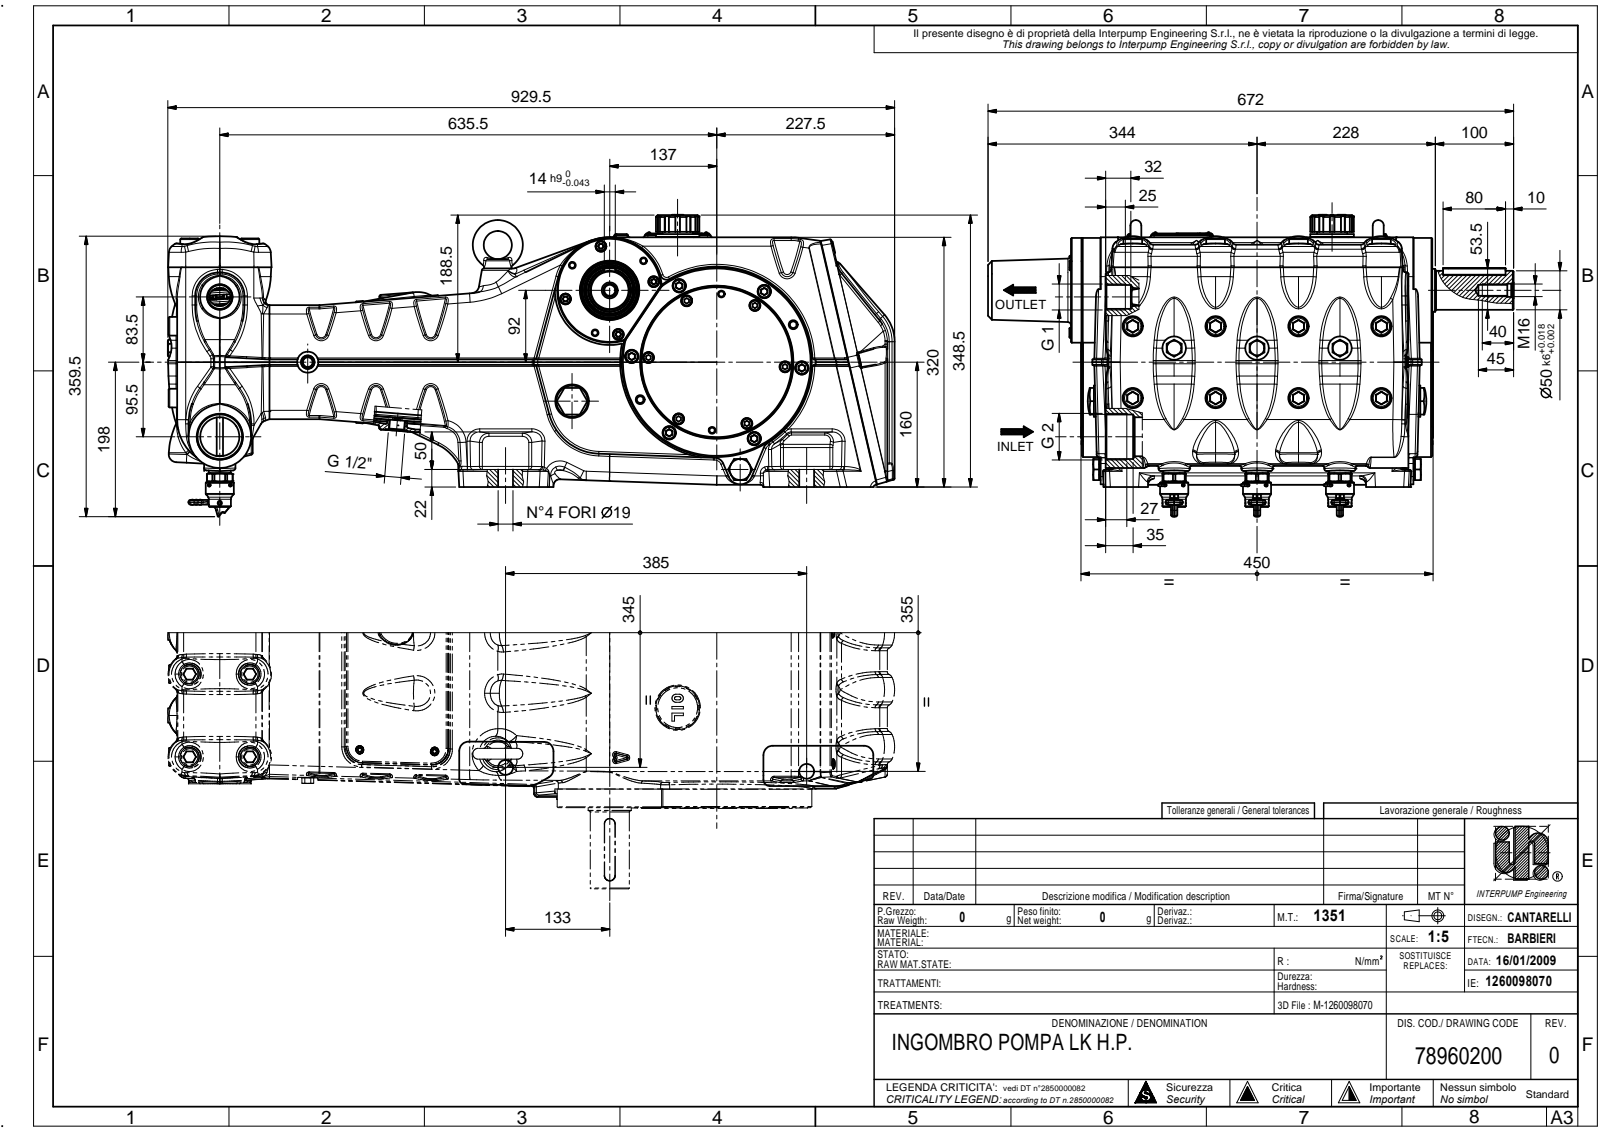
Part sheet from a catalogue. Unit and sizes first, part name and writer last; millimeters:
Units: millimetres
Overall size (bounding box): 929.09 × 672 × 386.71
Volume: 82 980 000 mm³ · Surface area: 3 509 000 mm²
Bodies: 134 solids, 11139 faces (0 planar, 0 cylindrical, 11139 other)
STEP written by: THINKDESIGN (CONFIG_CONTROL_DESIGN)
